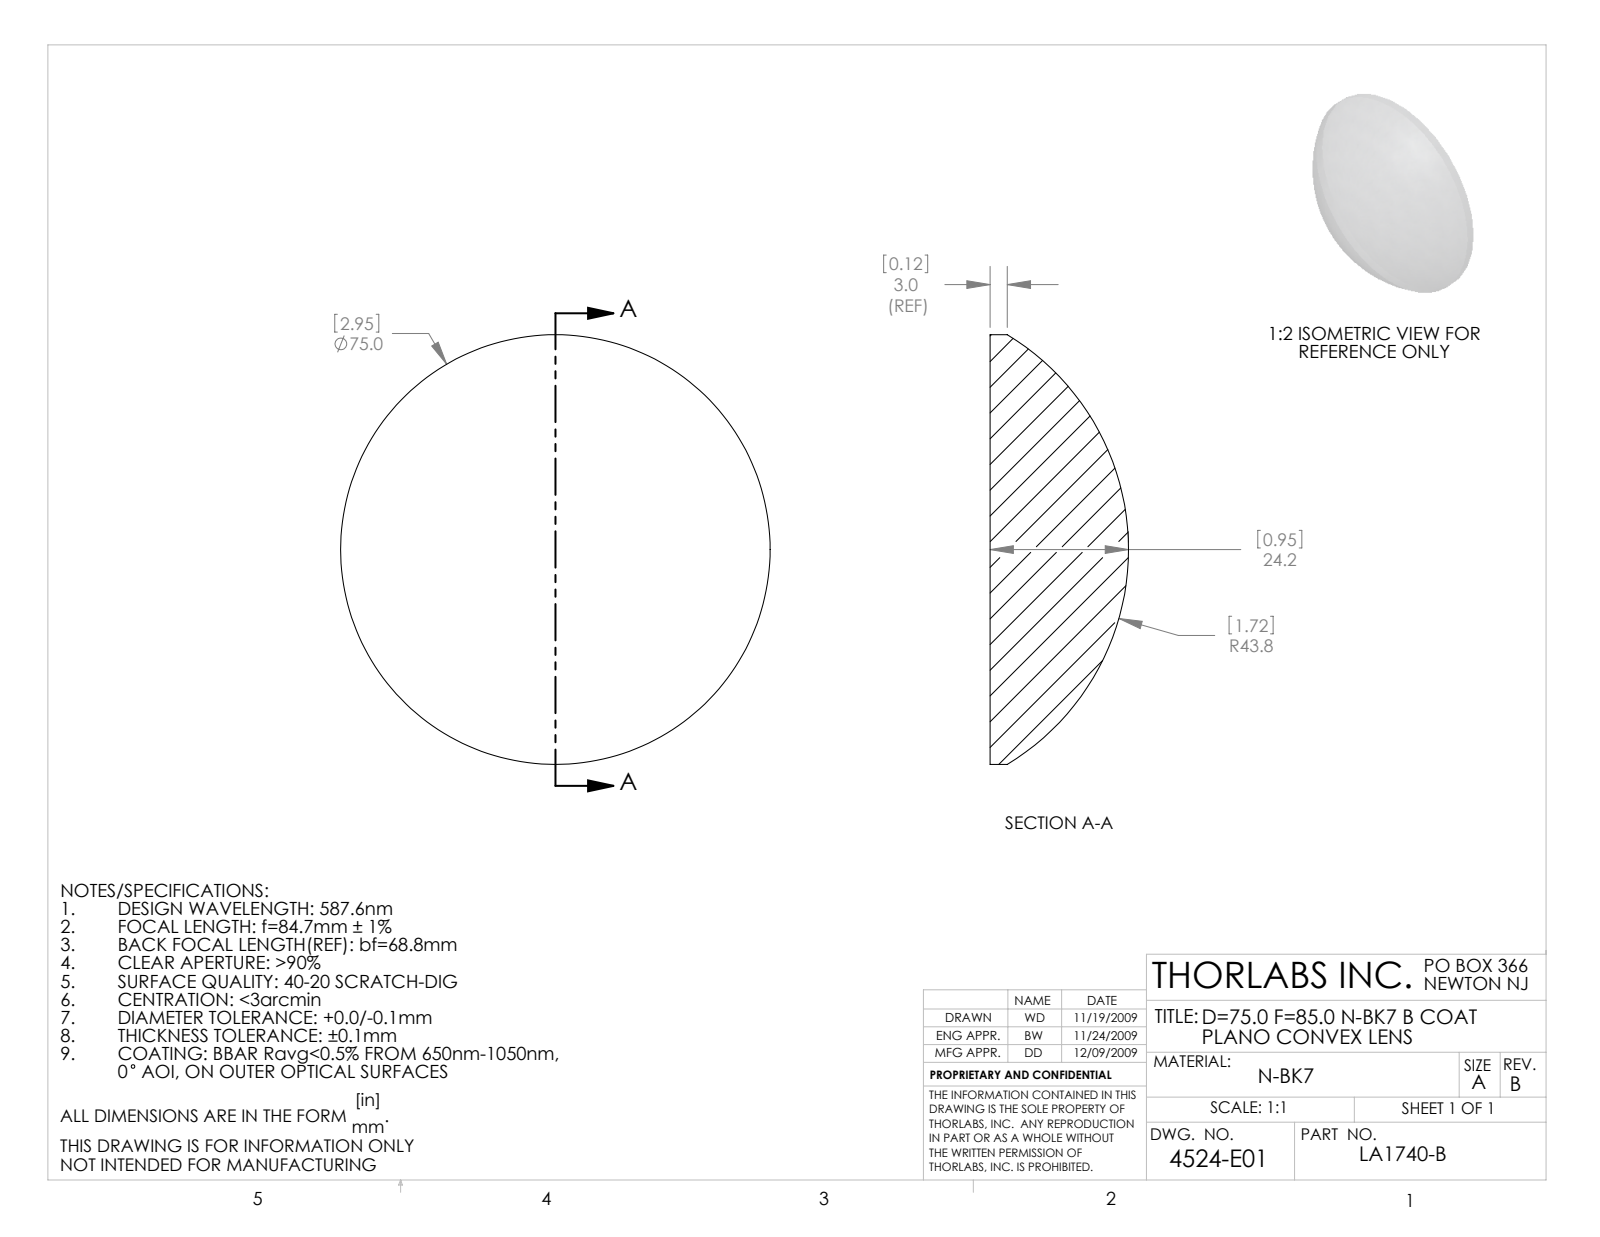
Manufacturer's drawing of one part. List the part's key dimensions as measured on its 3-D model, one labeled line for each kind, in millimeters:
Part name (STEP PRODUCT): 4524-E0W
STEP written by: SolidWorks 2009 (AUTOMOTIVE_DESIGN)
Units: millimetres
Bodies: 1 solid, 5 faces (1 planar, 2 cylindrical, 2 other)
Overall size (bounding box): 75 × 75 × 24.18
Volume: 65 003 mm³ · Surface area: 10 951 mm²
Round bosses / shafts (diameter × count): ⌀75 ×1
